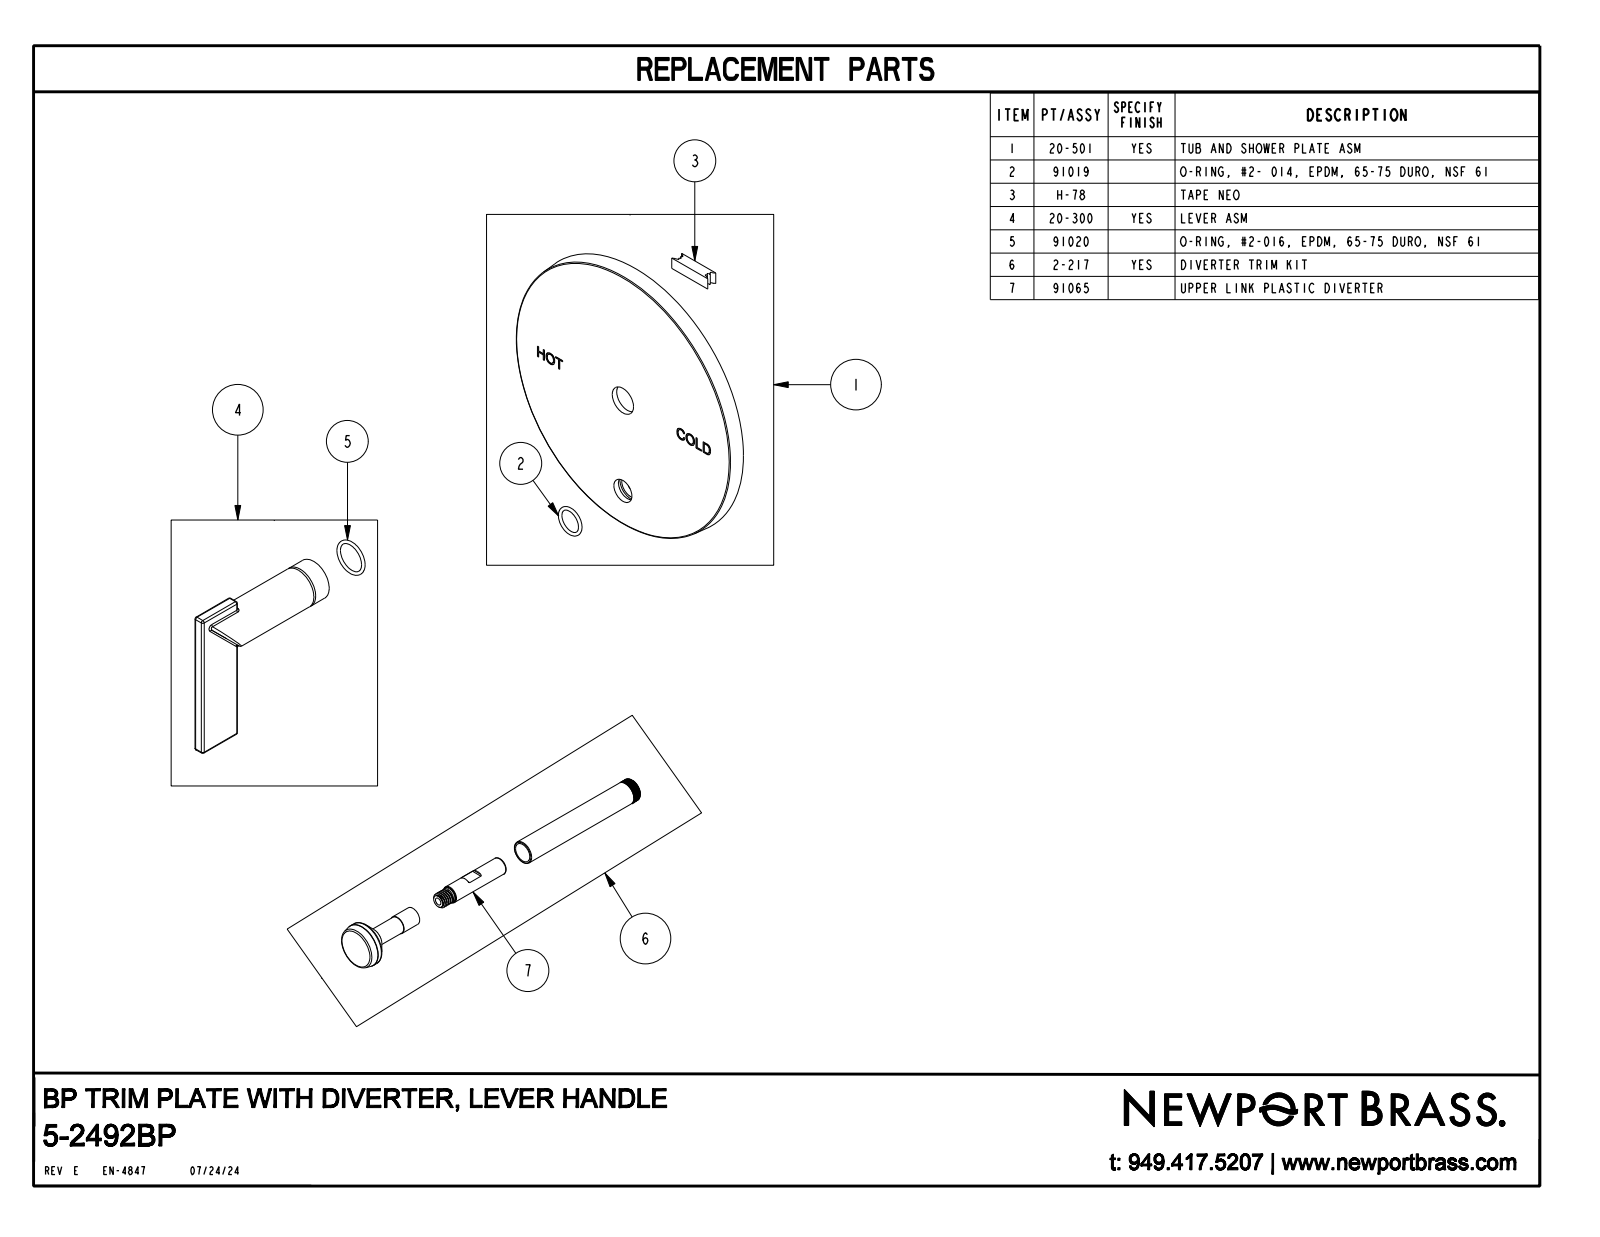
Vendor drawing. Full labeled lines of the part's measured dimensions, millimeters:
Part name (STEP PRODUCT): 30748; 91019; H-78; 20-501_ASM (+8 more)
STEP written by: CREO PARAMETRIC BY PTC INC, 2019352 (CONFIG_CONTROL_DESIGN)
Units: millimetres
Bodies: 16 solids, 1031 faces (258 planar, 412 cylindrical, 361 other)
Overall size (bounding box): 158.8 × 152.4 × 152.2
Volume: 107 200 mm³ · Surface area: 111 400 mm²
Round holes (diameter × count): ⌀1.3 ×2, ⌀2.8 ×1, ⌀3.6 ×1, ⌀3.8 ×1, ⌀6.7 ×1, ⌀7 ×1, ⌀8.1 ×1, ⌀8.8 ×1, ⌀9.1 ×1, ⌀9.1 ×1, ⌀9.5 ×1, ⌀9.7 ×1
Round bosses / shafts (diameter × count): ⌀25.4 ×1, ⌀22.9 ×1, ⌀21.8 ×1, ⌀17.3 ×1, ⌀15.7 ×1, ⌀13 ×1, ⌀12.9 ×1, ⌀12 ×1
Partial cylindrical surfaces — rounded edges, fillets, slot ends (radius × count): R1 ×16, R0.3 ×6, R1.1 ×6, R1.8 ×1, R3.5 ×1, R3.8 ×1, R4.3 ×1
Main face-to-face distances: 3.2, 6, 5.7, 8.9, 90.2, 84.5, 81.3, 36.1, 30.4, 27.2
Hole centre spacings: 55.1
